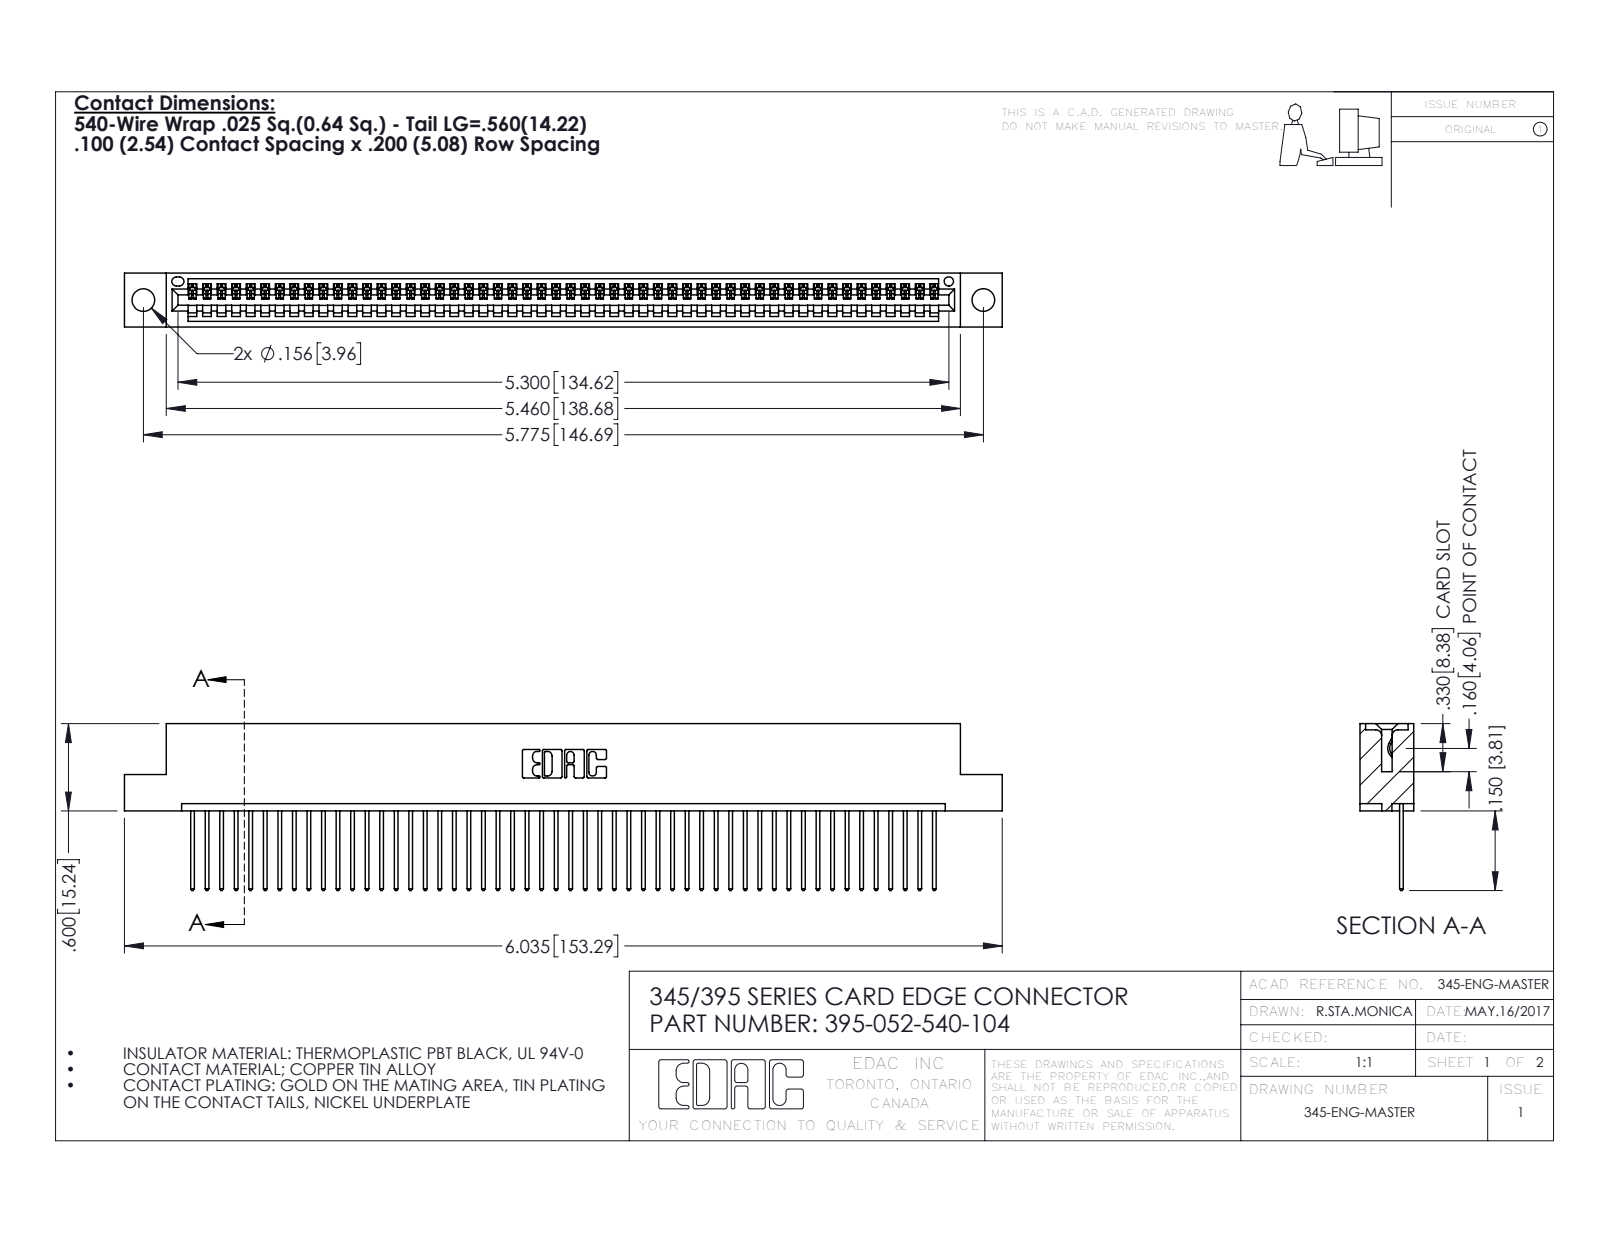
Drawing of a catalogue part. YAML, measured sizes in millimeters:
part_name: "395-052-540-104; 345-292-001_345-293-140; 345 Part_Flush Mounting Lugs - 0.156 Dia-TH"
step_written_by: "SolidWorks 2016 (CONFIG_CONTROL_DESIGN)"
units: millimeters
bodies: {solids: 53, faces: 3142, planar: 2160, cylindrical: 982, other: 0}
overall_size: [153.3, 29.1, 9.4]
volume: 14600
surface_area: 19880
round_holes:
  - {diameter: 4, count: 2}
  - {diameter: 1.6, count: 1}
partial_cylinders:
  - {radius: 0.2, count: 104}
  - {radius: 0.3, count: 104}
  - {radius: 0.3, count: 22}
  - {radius: 0.2, count: 6}
  - {radius: 0.8, count: 6}
  - {radius: 0.7, count: 3}
  - {radius: 0.8, count: 2}
  - {radius: 1, count: 2}
face_to_face_distances: [7.6, 1.8, 9.4, 2.5, 6.9, 0.6, 5.1, 5.7, 3.8, 1.8]
hole_center_spacings: [6.9, 140.7, 146.7]
